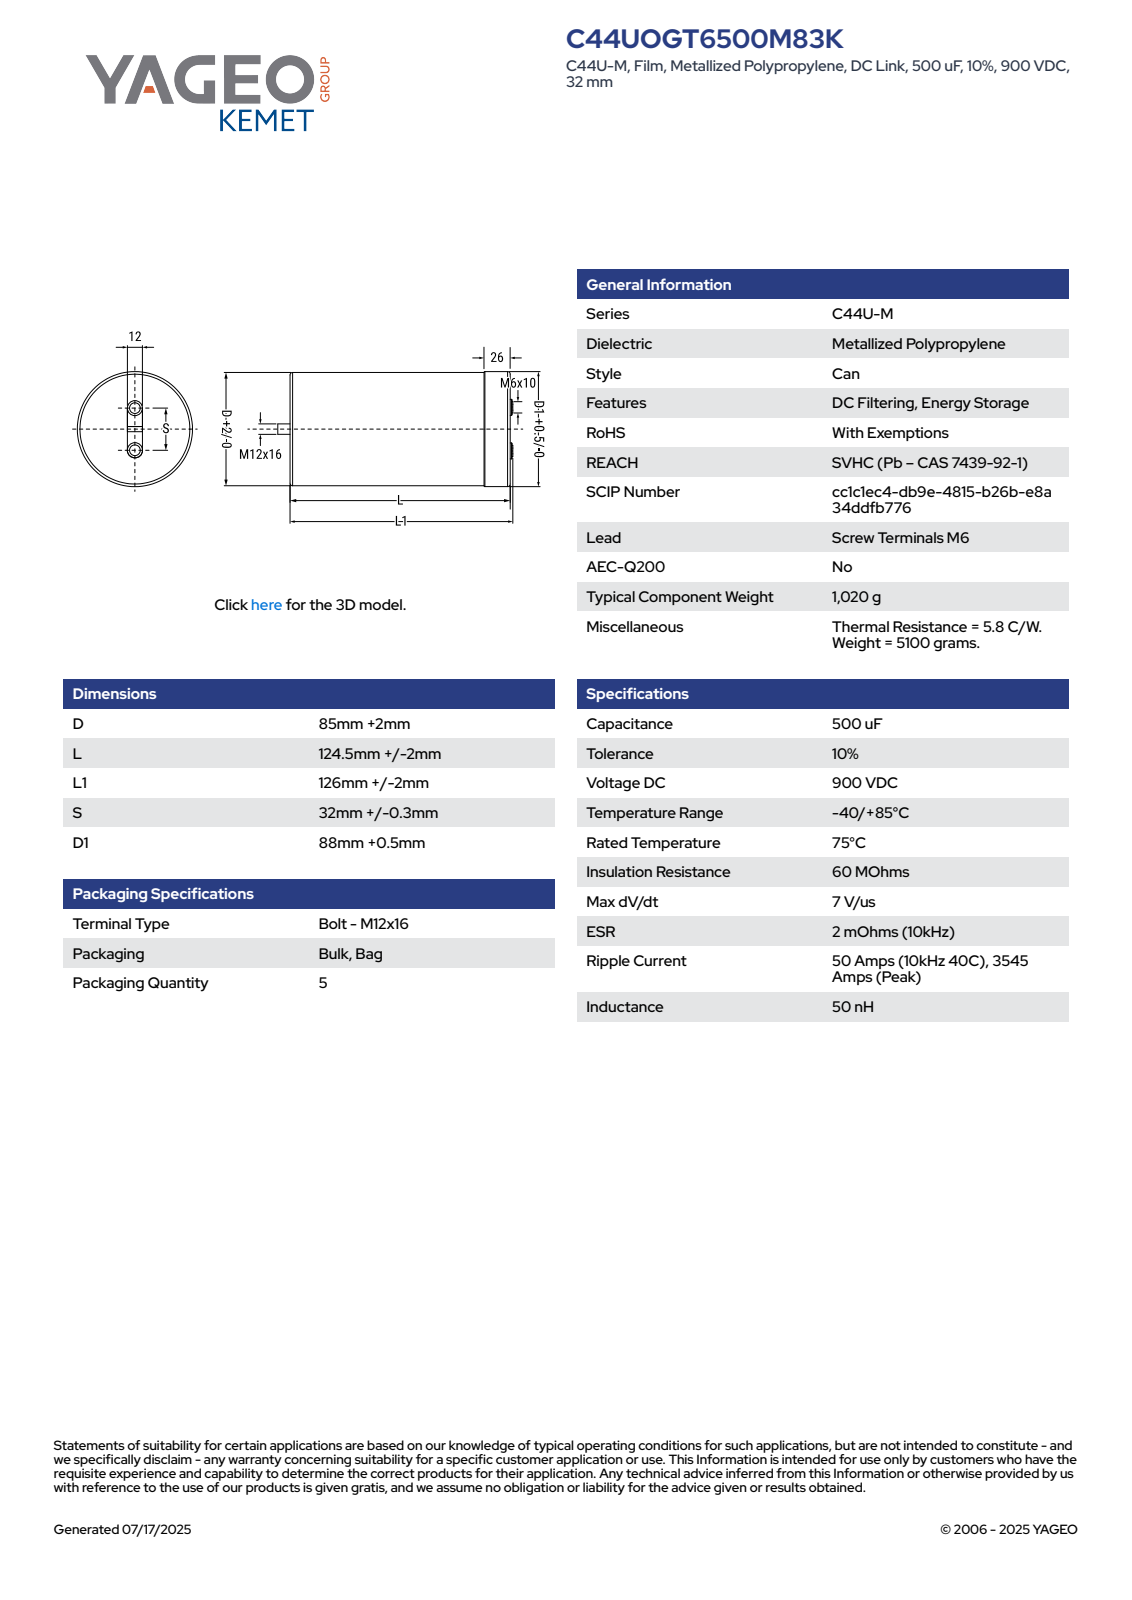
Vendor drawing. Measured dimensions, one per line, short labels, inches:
name: CFP_C44UMR_85X124.5_D87L126.5S32L1128D188.5
written by: SolidWorks 2014 (AUTOMOTIVE_DESIGN)
unit: in
bodies: 1 solid, 84 faces (32 planar, 21 cylindrical, 31 other)
size: 5.669 × 3.484 × 3.484
volume: 46.31 in³; area: 74.54 in²
holes: 2× ⌀0.236
bosses: 3× ⌀0.472, 2× ⌀0.394, 1× ⌀3.484, 1× ⌀3.425
rounds: 1× R1.713
face distances: 4.98, 3.957, 1.024, 0.63, 4.587, 5.61, 5.669, 5.039, 1.083, 0.059
hole spacings: 1.26
